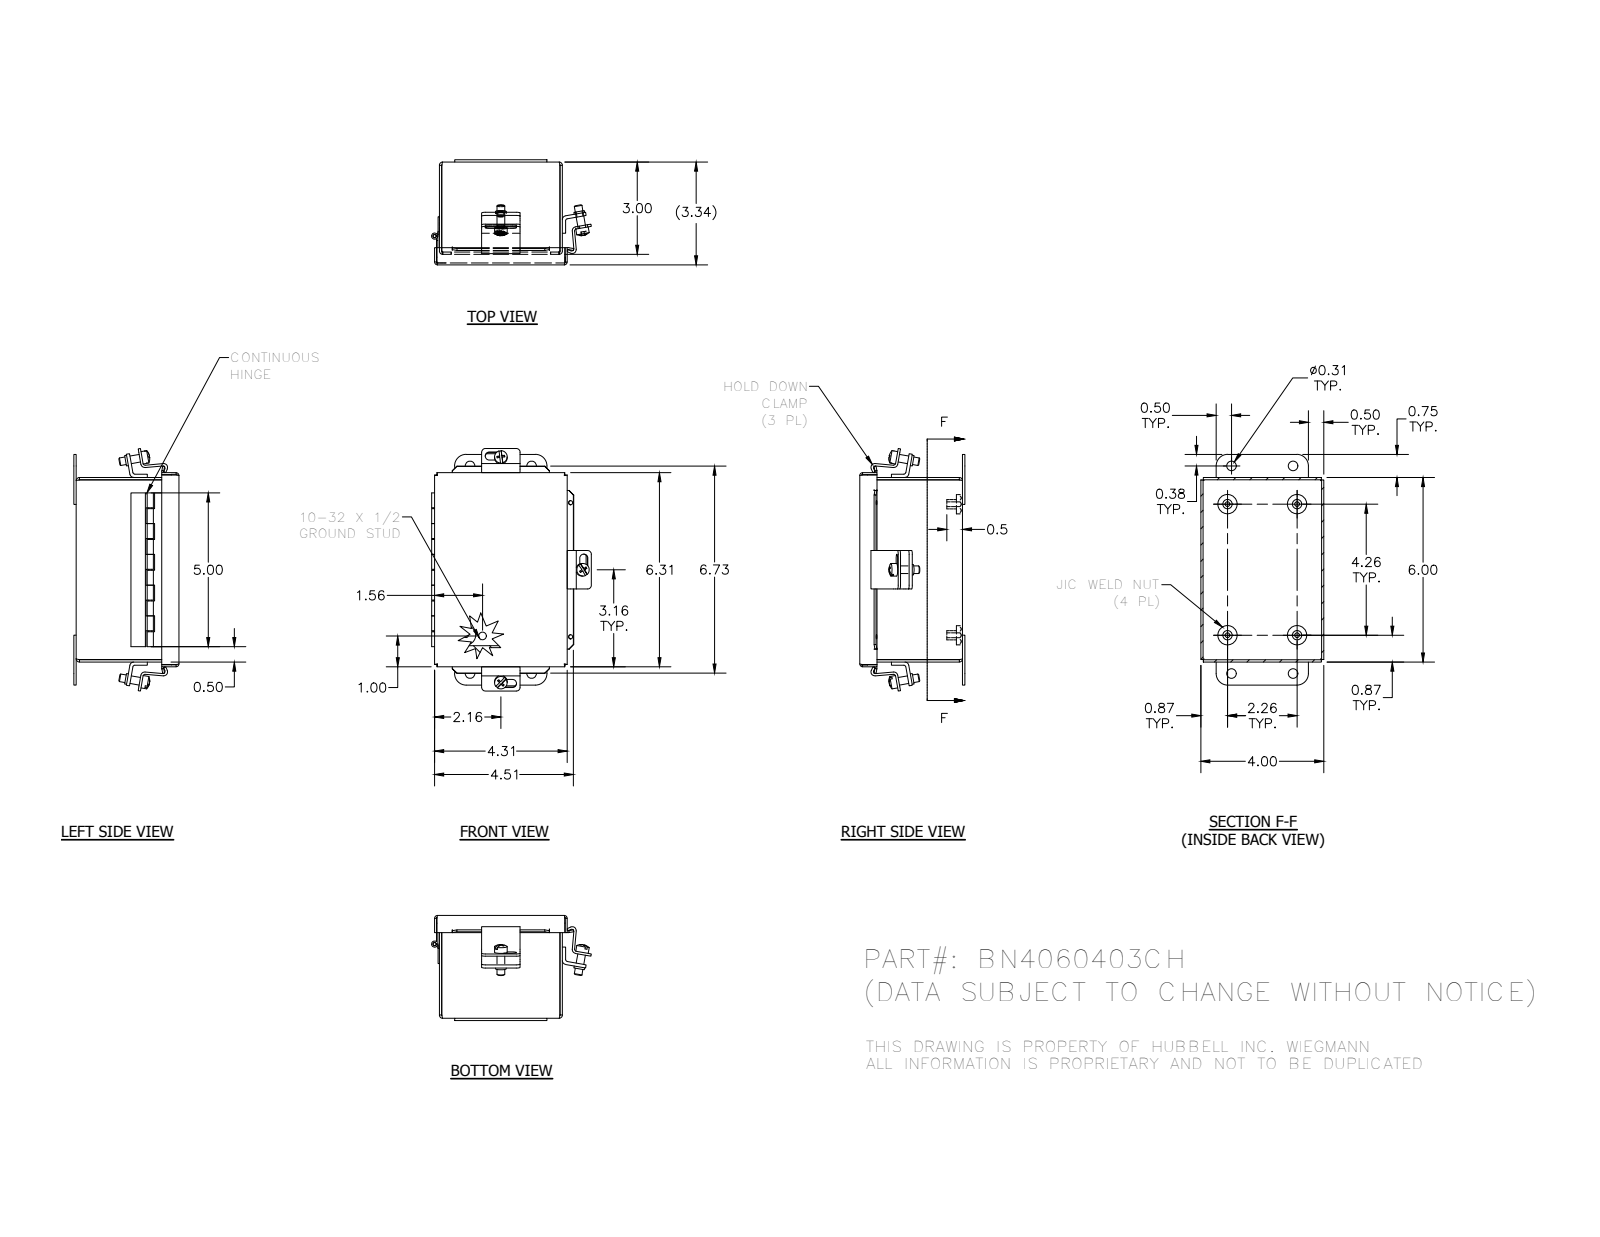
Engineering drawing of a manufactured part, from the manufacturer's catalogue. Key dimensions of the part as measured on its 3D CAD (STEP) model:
Part name (STEP PRODUCT): B_0604CH_LID; 316160; 38811; 3499 (+8 more)
STEP written by: Autodesk Inventor 2016 (AUTOMOTIVE_DESIGN)
Units: millimetres
Bodies: 17 solids, 394 faces (255 planar, 91 cylindrical, 48 other)
Overall size (bounding box): 190.5 × 129.18 × 82.78
Volume: 203 894 mm³ · Surface area: 218 951 mm²
Round holes (diameter × count): ⌀3.96 ×4, ⌀7.87 ×4, ⌀3.56 ×2, ⌀2.96 ×1, ⌀4.98 ×1
Round bosses / shafts (diameter × count): ⌀15.88 ×4, ⌀7.62 ×4, ⌀6.35 ×2, ⌀10.4 ×1, ⌀8.74 ×1, ⌀5.08 ×1, ⌀4.83 ×1, ⌀2.54 ×1
Partial cylindrical surfaces — rounded edges, fillets, slot ends (radius × count): R1.19 ×8, R3.07 ×8, R1.98 ×4, R3.17 ×4, R3.48 ×4, R9.53 ×4, R0.79 ×3, R1.6 ×3
Main face-to-face distances: 1.88, 1.5, 99.72, 79.38, 80.88, 77.5, 79, 150.52, 101.6, 97.84
Hole centre spacings: 31.91, 139.74, 50.8, 57.15, 62.62, 62.63, 107.95, 122.14
